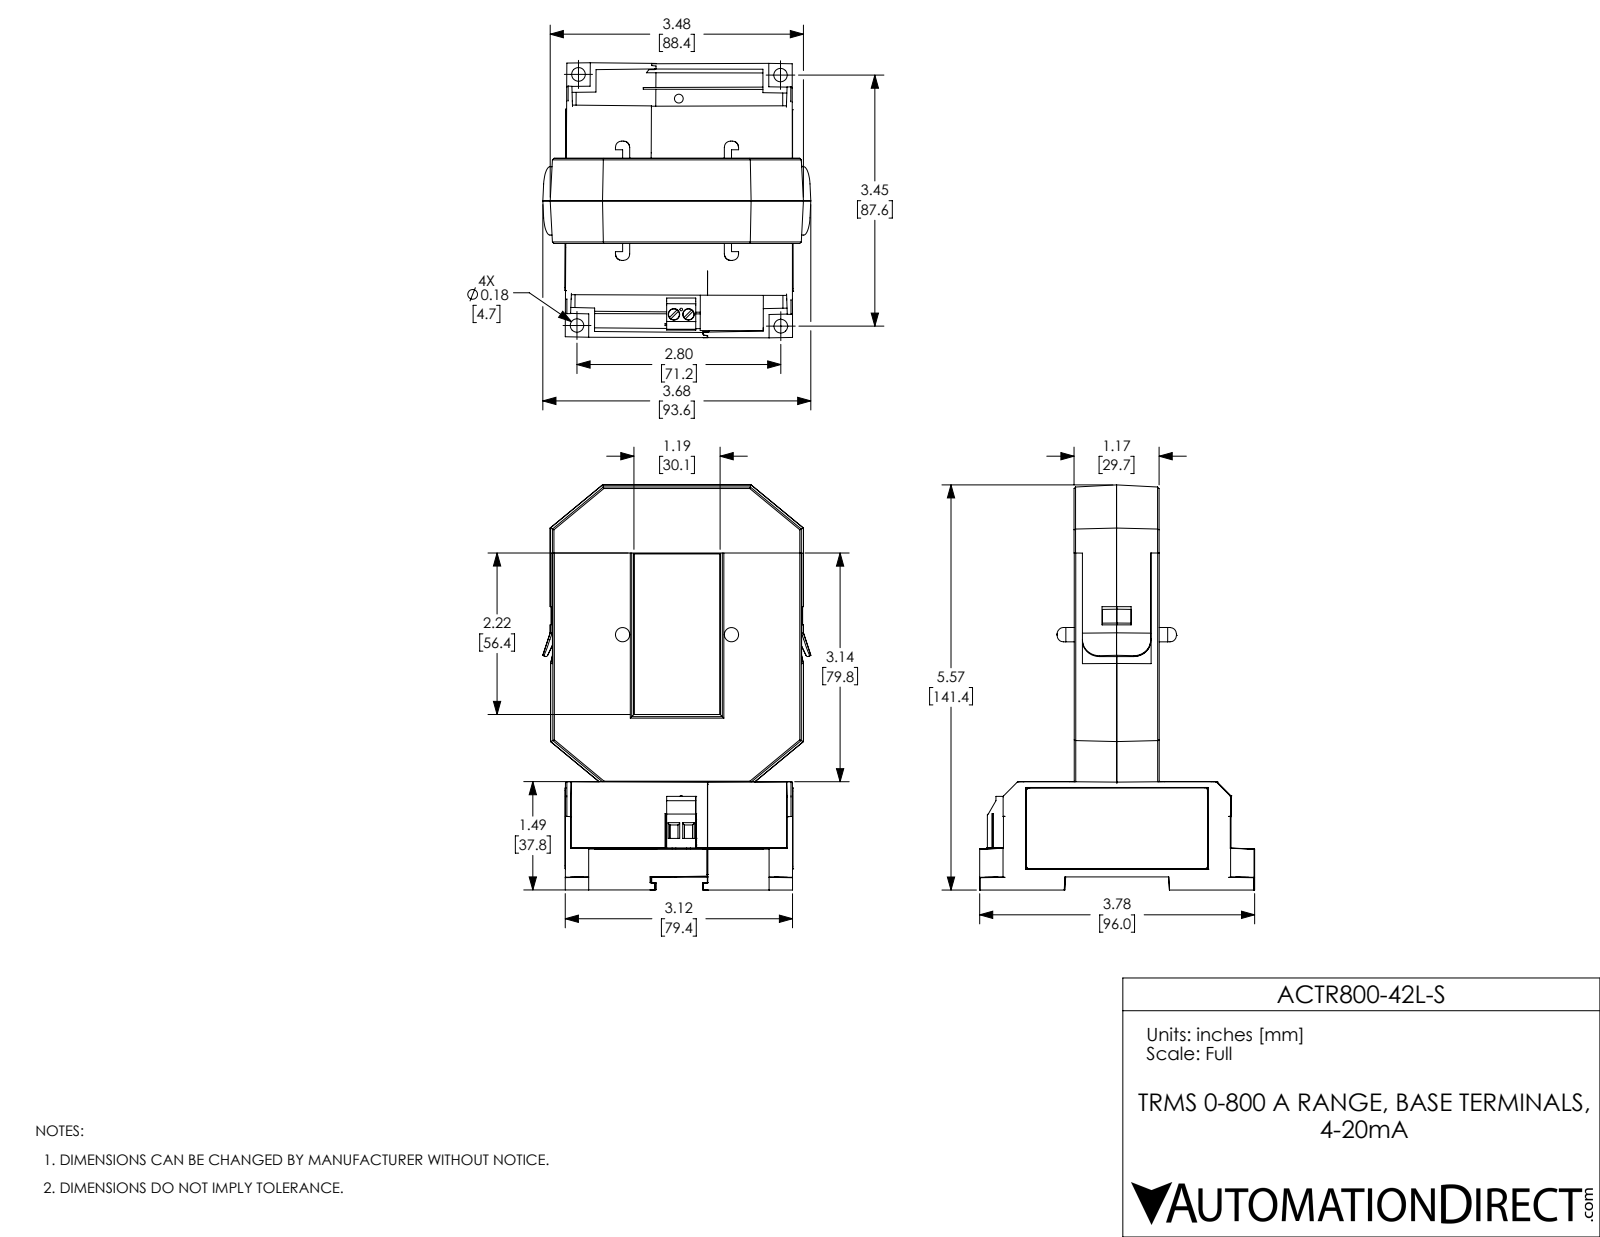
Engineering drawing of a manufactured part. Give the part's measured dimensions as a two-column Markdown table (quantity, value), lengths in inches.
| quantity | value |
| --- | --- |
| part name | ACTR800-42L-S |
| STEP written by | SolidWorks 2017 (AUTOMOTIVE_DESIGN) |
| units | inches |
| bodies | 15 solids, 1439 faces (1182 planar, 144 cylindrical, 113 other) |
| overall size | 5.569 × 3.781 × 3.684 |
| volume | 7.995 in³ |
| surface area | 222.6 in² |
| round holes (diameter × count) | 0.157 × 2, 0.256 × 2 |
| round bosses / shafts (diameter × count) | 0.197 × 2, 0.15 × 2, 0.051 × 2, 0.018 × 1 |
| partial cylindrical surfaces (radius × count) | 0.02 × 30, 0.039 × 12, 0.006 × 10, 0.05 × 8, 0.025 × 6, 0.008 × 4, 0.01 × 4, 0.02 × 4 |
| main face-to-face distances | 0.071, 1.097, 1.168, 1.026, 0.081, 0.585, 0.075, 0.08, 2.328, 1.095 |
| hole center spacings | 0.2, 0.42, 1.563, 1.57, 1.581, 1.604 |
